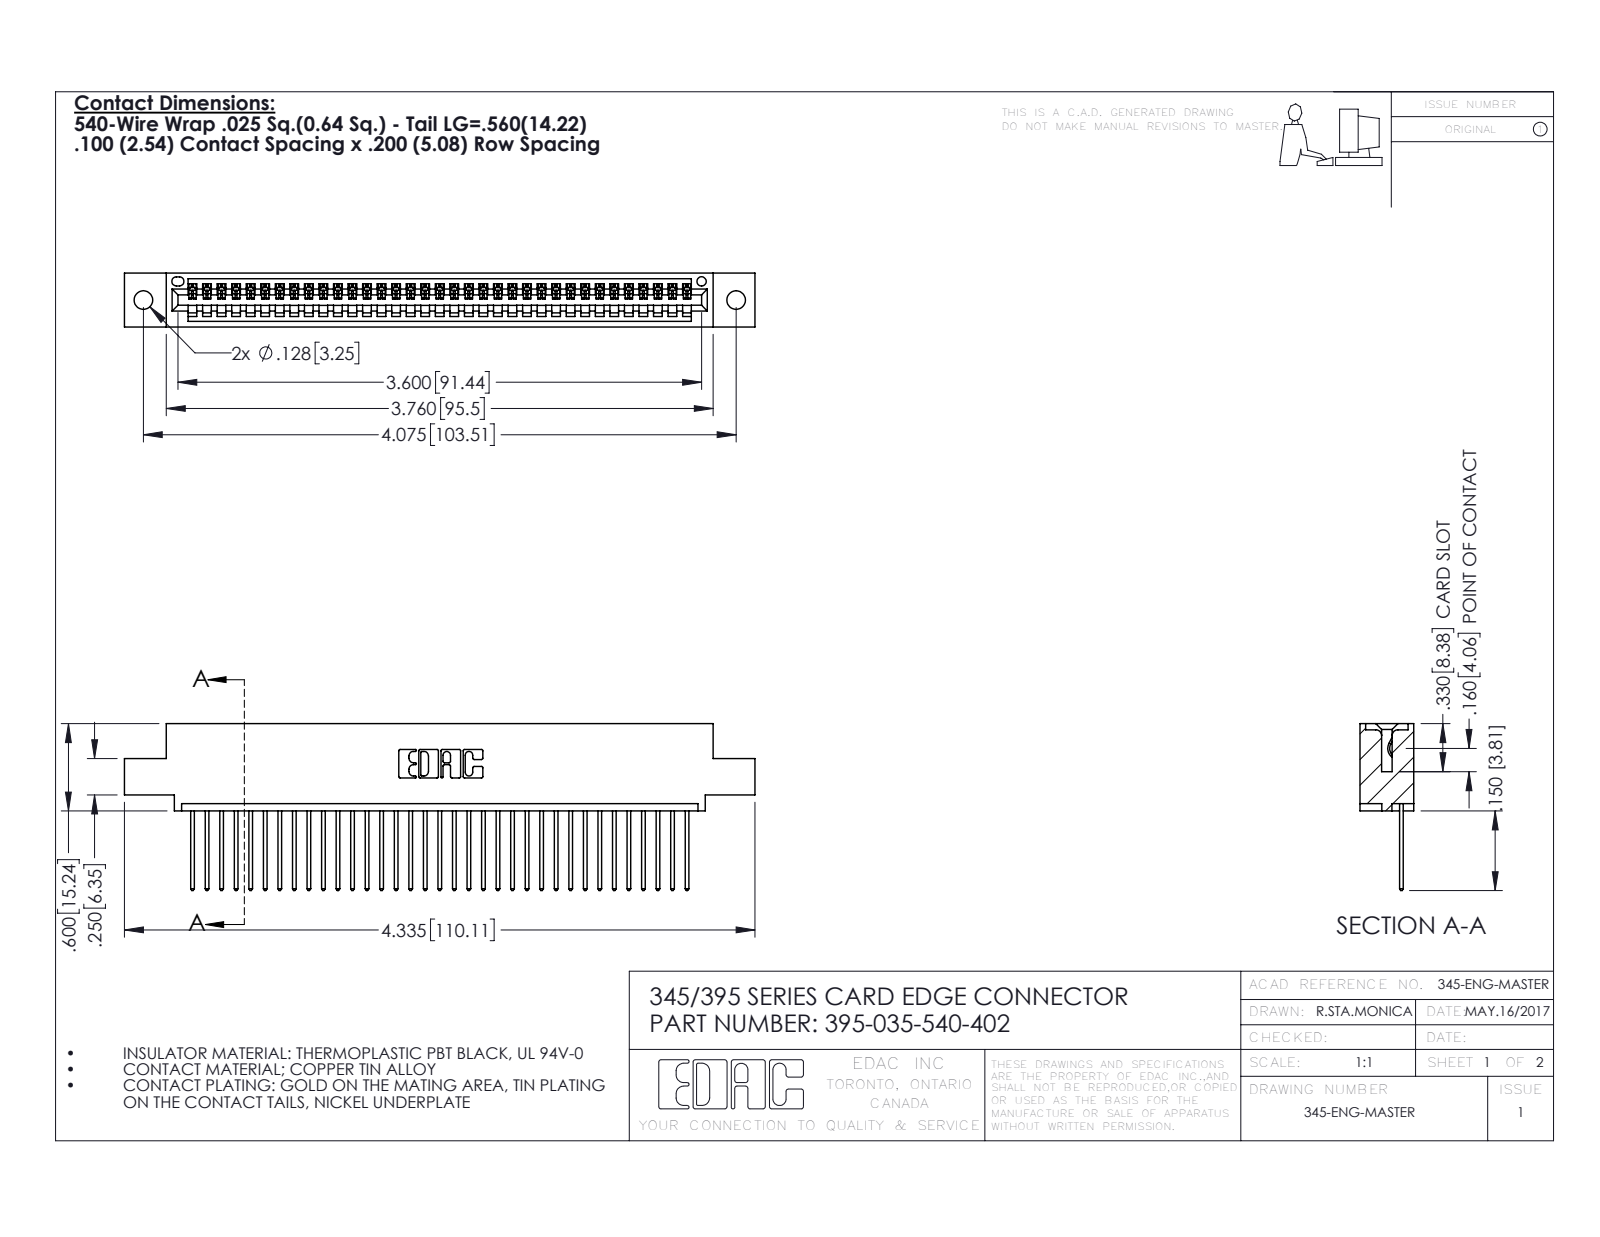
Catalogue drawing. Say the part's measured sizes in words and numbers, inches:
The part is named "345-292-001_345-293-140; 395-035-540-402; 345 Part_0.110 Offset - 0.128 Dia". Its 3-D file was written by "SolidWorks 2016 (CONFIG_CONTROL_DESIGN)". It is 36 solids with 2160 faces: 1484 planar, 676 cylindrical and 0 other. Overall it measures 4.335 by 1.147 by 0.37 inches. Its volume is 0.631 cubic inches and its surface area 21.38 square inches. Round holes: 2 of diameter 0.128, 1 of diameter 0.064. Partial cylindrical surfaces (rounded edges, fillets, slot ends): 70 of radius 0.006, 70 of radius 0.01, 22 of radius 0.01, 6 of radius 0.007, 6 of radius 0.031, 3 of radius 0.026, 2 of radius 0.031, 2 of radius 0.04. The main face-to-face distances are 0.298, 0.072, 0.37, 0.098, 0.272, 0.025, 0.2, 0.225, 0.149, 0.072. The hole center spacings are 0.27, 3.839, 4.075.
